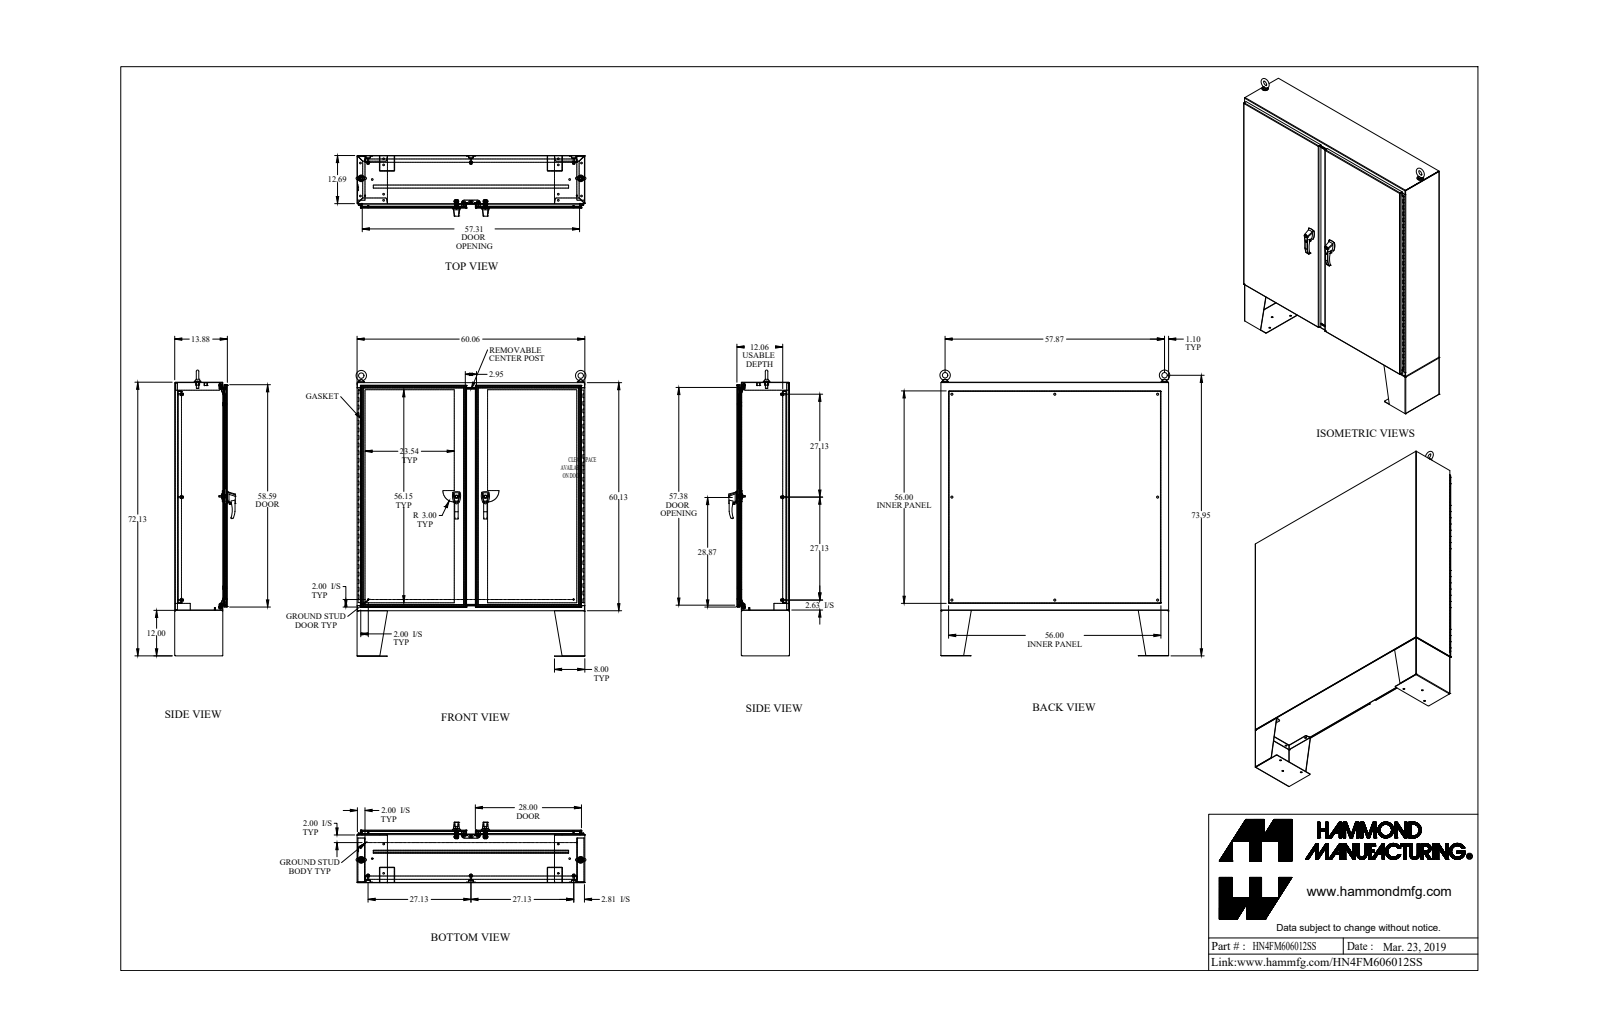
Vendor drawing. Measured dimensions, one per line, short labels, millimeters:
name: HN4FM606012SS
written by: SolidWorks 2018 (AUTOMOTIVE_DESIGN)
unit: mm
bodies: 130 solids, 3760 faces (1740 planar, 1659 cylindrical, 361 other)
size: 1913.2 × 1539.4 × 406.1
volume: 28 630 000 mm³; area: 22 530 000 mm²
holes: 20× ⌀7.7, 14× ⌀11.1, 8× ⌀7.8, 8× ⌀8.9, 8× ⌀14.3, 6× ⌀6.4, 6× ⌀11.3, 4× ⌀7.1, 4× ⌀8, 4× ⌀9.9, 3× ⌀5.1, 3× ⌀8
bosses: 10× ⌀25.4, 8× ⌀16.5, 8× ⌀9.5, 8× ⌀8.4, 4× ⌀19.1, 4× ⌀15.9, 4× ⌀11.2, 4× ⌀9.4
rounds: 33× R12.7, 32× R0.5, 32× R3.2, 28× R1.5, 27× R1.2, 27× R3.6, 12× R0.8, 12× R2.3
face distances: 2.4, 350, 347.6, 304.7, 3.2, 352.4, 45.3, 42.8, 307.2, 42.1
hole spacings: 152.4, 304.8, 457.2, 609.6, 1378, 762, 1486.2, 40.9
